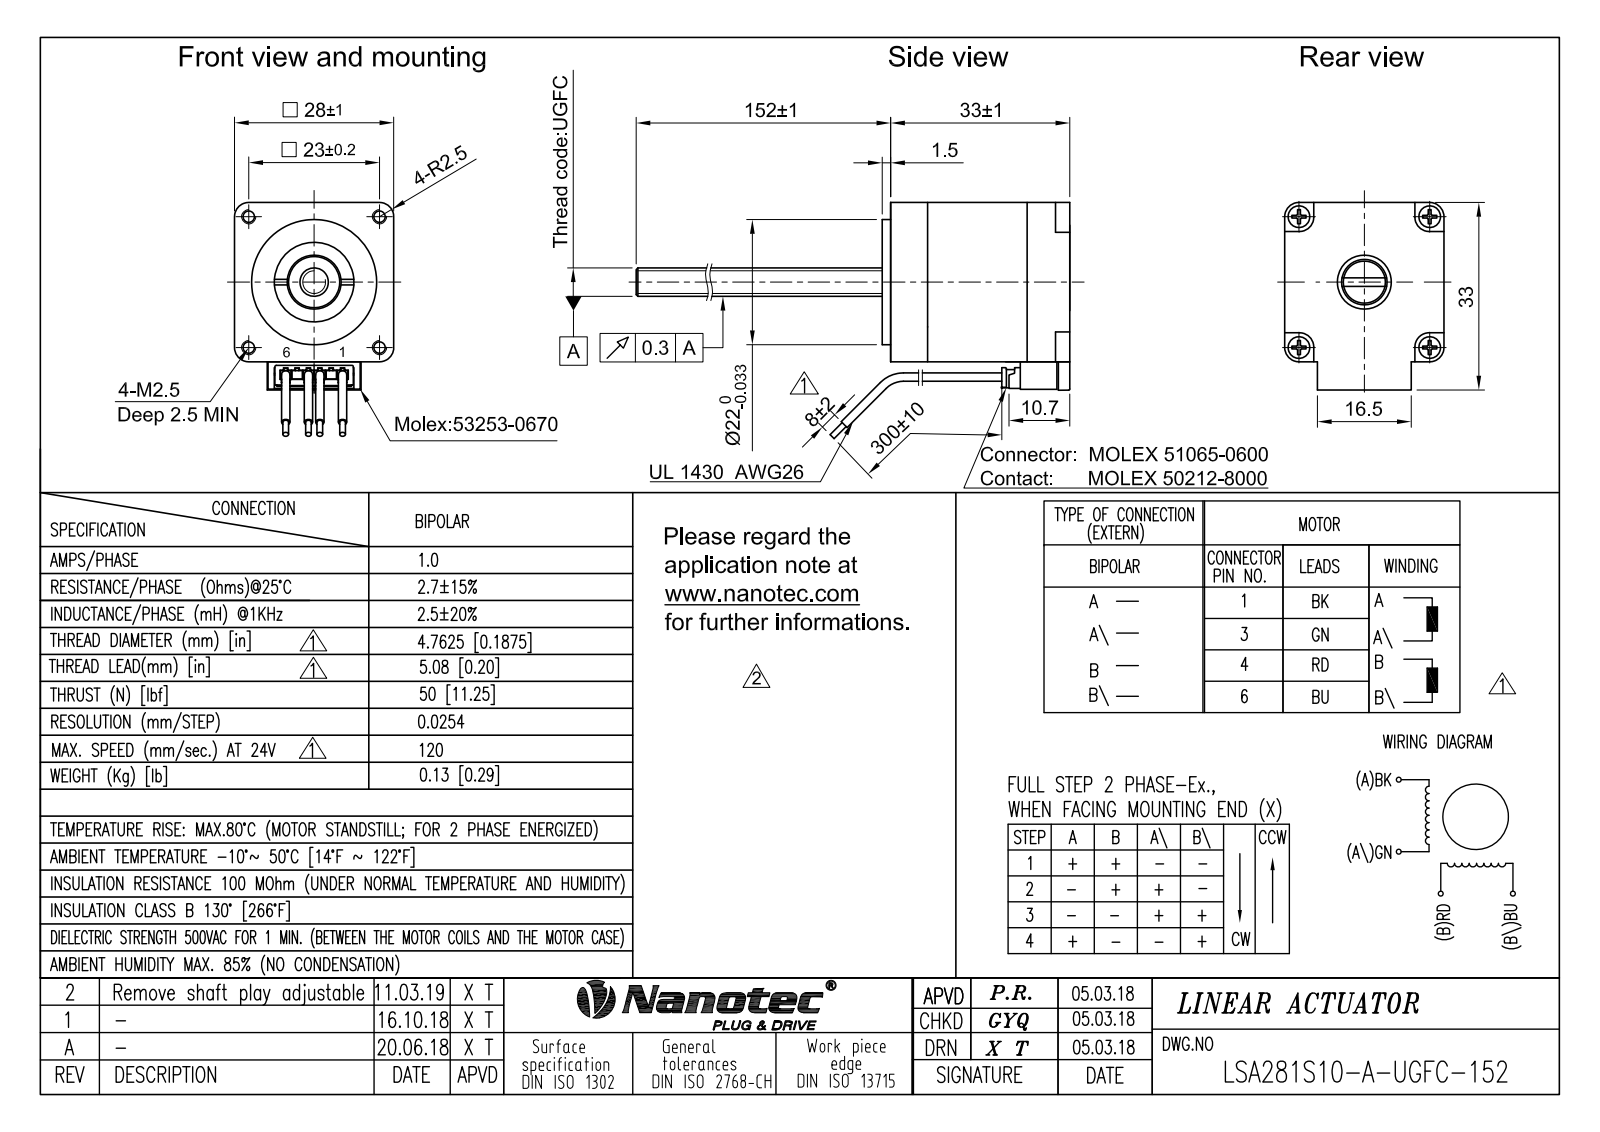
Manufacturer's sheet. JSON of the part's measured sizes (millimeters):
{"part_name": "零件28", "step_written_by": "Autodesk Inventor 2013 (CONFIG_CONTROL_DESIGN)", "units": "millimeters", "bodies": {"solids": 2, "faces": 436, "planar": 321, "cylindrical": 39, "other": 76}, "overall_size": [185.3, 33, 28], "volume_mm3": 29379, "surface_area_mm2": 9040, "round_holes": [[2.05, 4], [8, 1], [9.5, 1]], "round_bosses_or_shafts": [[22, 1], [4.76, 1]], "partial_cylinders_radius": [[0.5, 5], [2.5, 4], [0.6, 3], [1, 2], [19, 1]], "face_to_face_distances": [28, 33.3, 1.5, 34.8, 0.4, 0.5, 32.8, 1, 2, 32.4], "hole_center_spacings": [16.26, 23, 32.53]}
